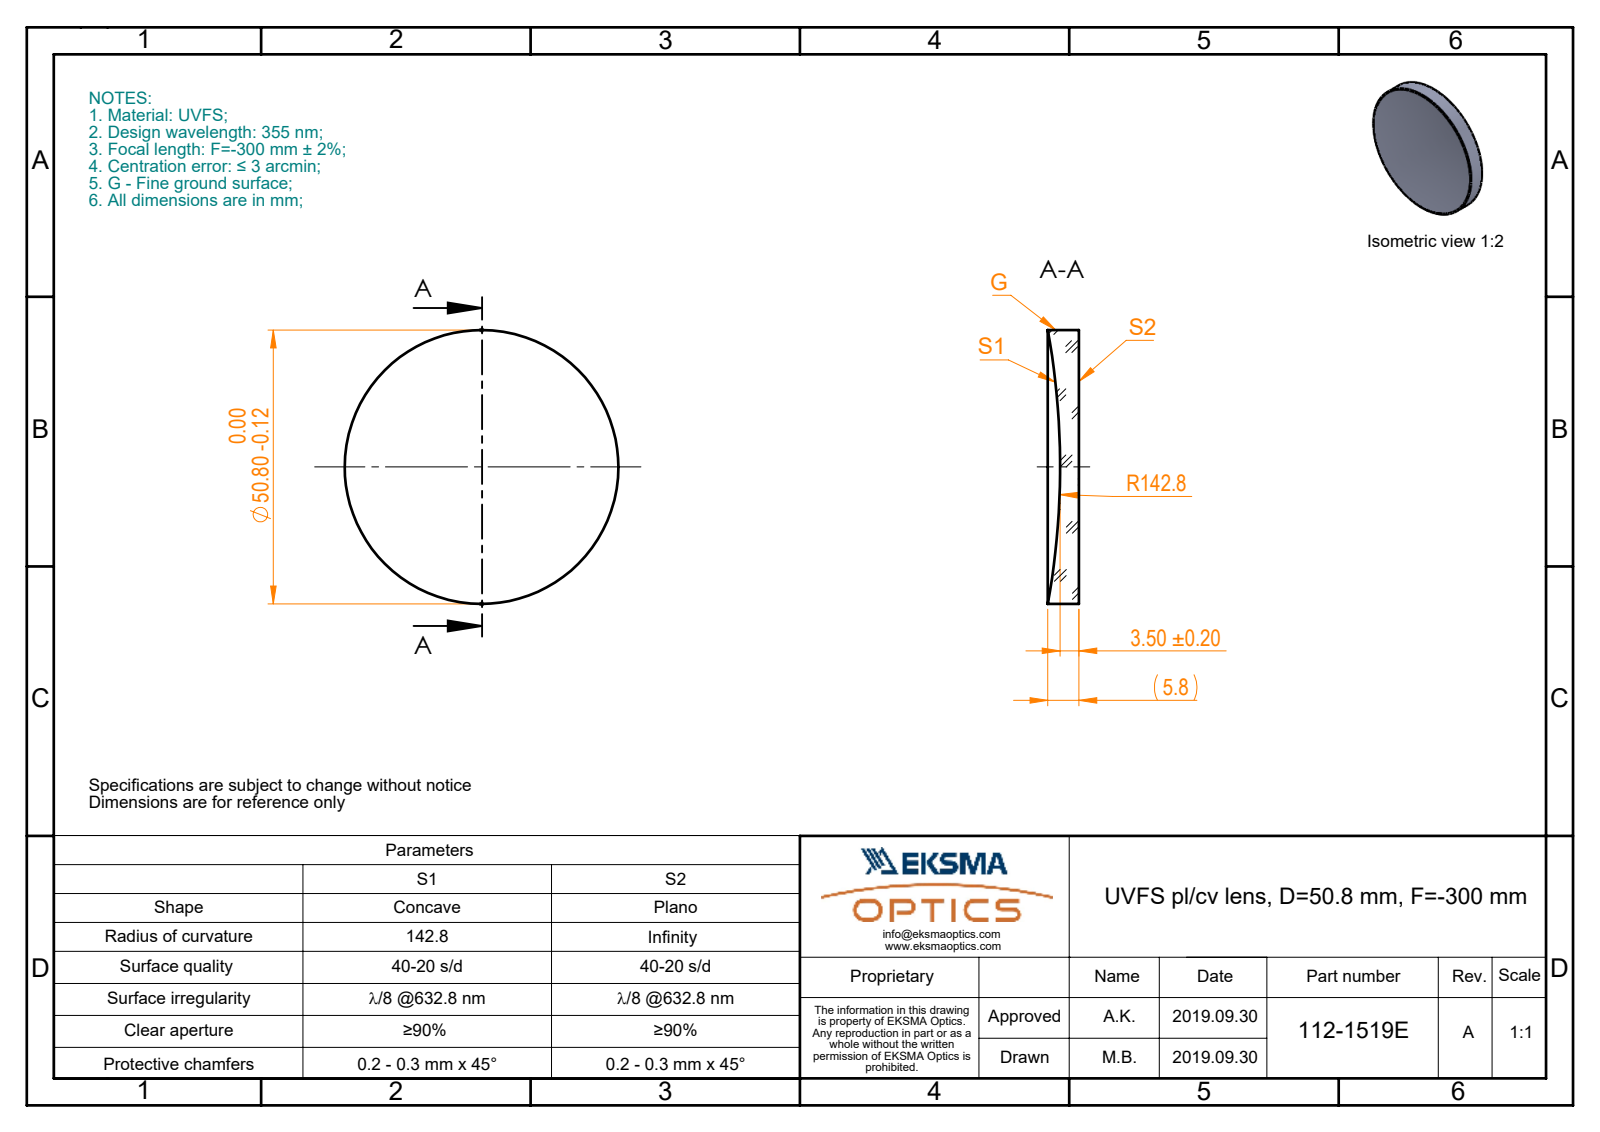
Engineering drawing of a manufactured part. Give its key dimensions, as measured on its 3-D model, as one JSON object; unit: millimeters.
{"part_name": "112-1519E UVFS pl-cv 50.8 F-300", "step_written_by": "SolidWorks 2019 (CONFIG_CONTROL_DESIGN)", "units": "millimeters", "bodies": {"solids": 1, "faces": 4, "planar": 1, "cylindrical": 2, "other": 1}, "overall_size": [50.8, 50.8, 5.78], "volume_mm3": 9395, "surface_area_mm2": 4992, "round_bosses_or_shafts": [[50.8, 1]]}
